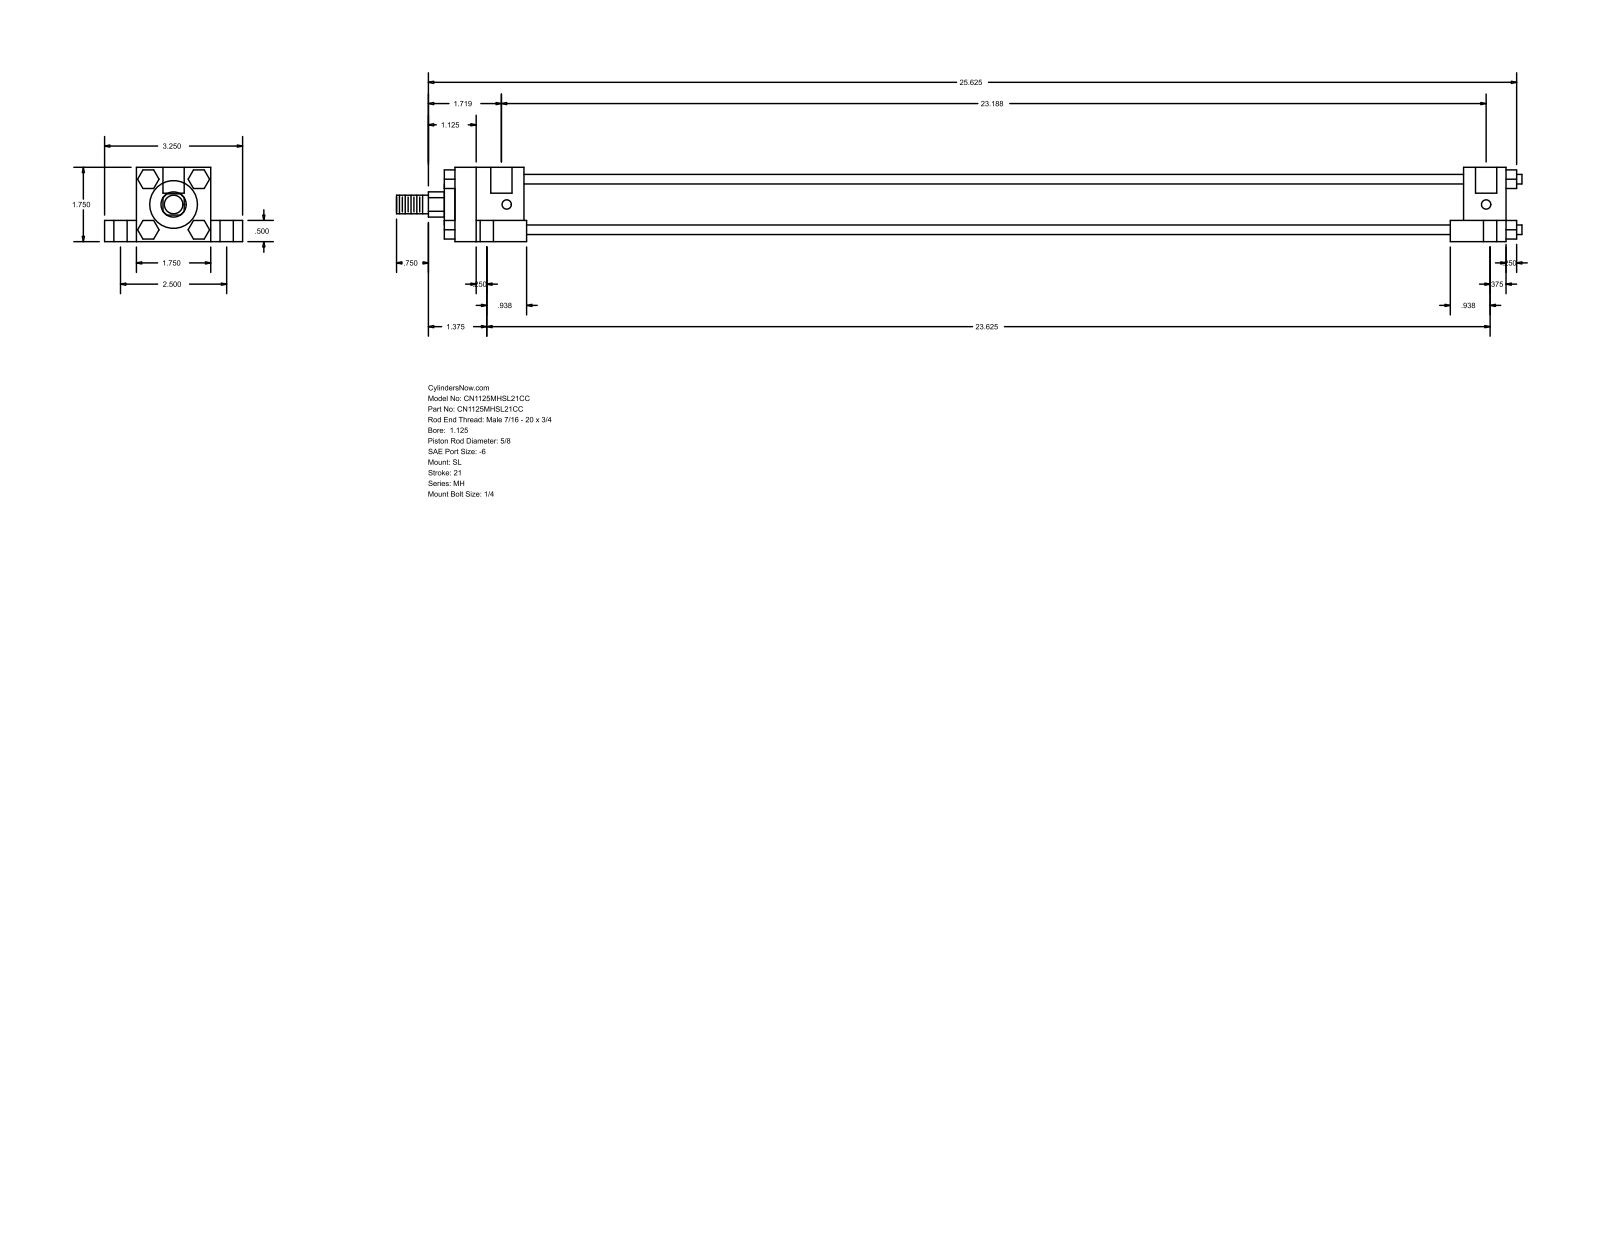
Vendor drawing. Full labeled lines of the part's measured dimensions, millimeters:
Part name (STEP PRODUCT): MH_SL__0112_0.625
STEP written by: GSSL Pune (CONFIG_CONTROL_DESIGN)
Units: millimetres
Bodies: 0 solids, 150 faces (114 planar, 36 cylindrical, 0 other)
Overall size (bounding box): 673.1 × 82.55 × 44.45
Round holes (diameter × count): ⌀5.56 ×4, ⌀7.94 ×4, ⌀14.29 ×4, ⌀12.7 ×2
Round bosses / shafts (diameter × count): ⌀5.71 ×4, ⌀34.92 ×1, ⌀28.57 ×1, ⌀15.88 ×1, ⌀11.11 ×1
Partial cylindrical surfaces — rounded edges, fillets, slot ends (radius × count): R7.54 ×1
Main face-to-face distances: 44.46, 31.76, 19.04, 12.7, 63.5, 11.11, 47.62, 25.4, 561.97, 587.37
Hole centre spacings: 31.84, 32.23, 32.93, 63.5, 585.79, 589.03, 592.19, 595.37
